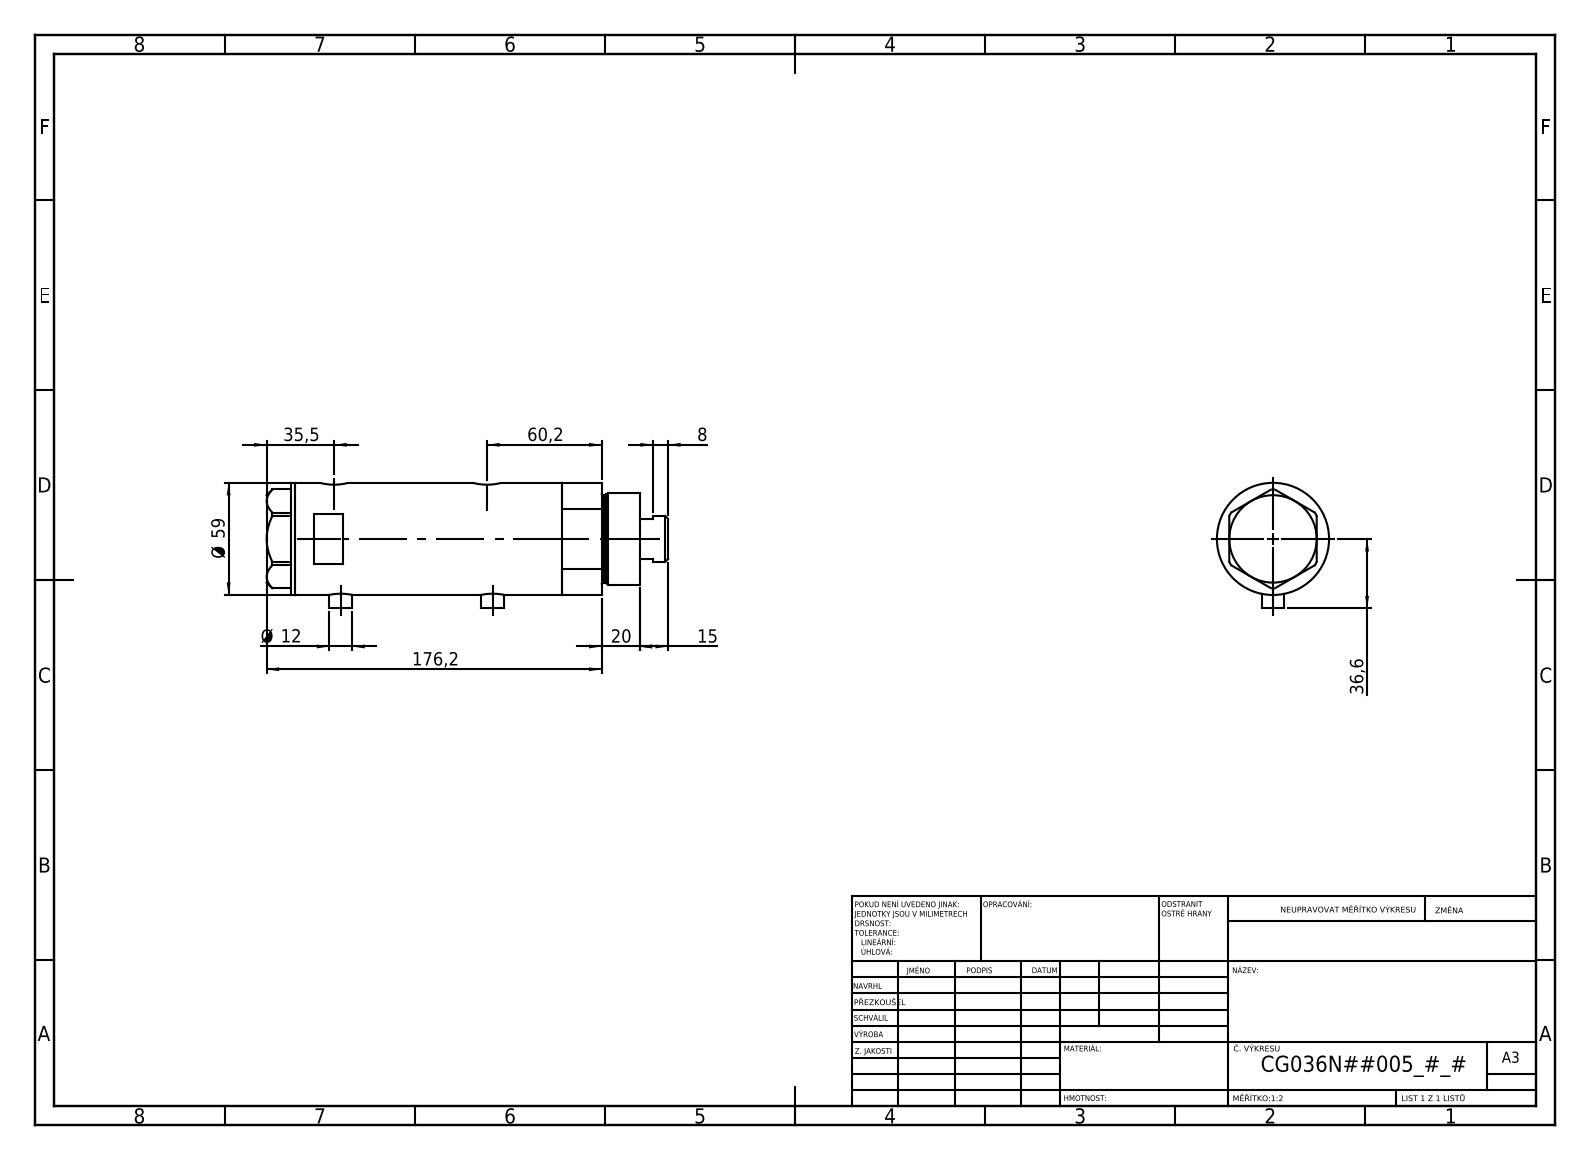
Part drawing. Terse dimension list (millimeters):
name: V270CG_BACK; V270CG_FRONT; V270CG_VC; V270CG_MIDDLE
written by: SolidWorks 2019 (CONFIG_CONTROL_DESIGN)
unit: mm
bodies: 4 solids, 120 faces (51 planar, 49 cylindrical, 20 other)
size: 211.2 × 66.1 × 59
volume: 502 159 mm³; area: 101 530 mm²
holes: 2× ⌀9.73, 2× ⌀12.5, 2× ⌀15, 1× ⌀8.5, 1× ⌀25, 1× ⌀26.5, 1× ⌀36, 1× ⌀40, 1× ⌀52
bosses: 2× ⌀12, 1× ⌀59, 1× ⌀48, 1× ⌀46, 1× ⌀24
face distances: 102.2, 23.5, 78.7, 15, 38.5, 117.2, 2, 196.2, 181.2, 157.7
hole spacings: 2.9, 3.5, 77, 79.9, 80.5, 83.4
